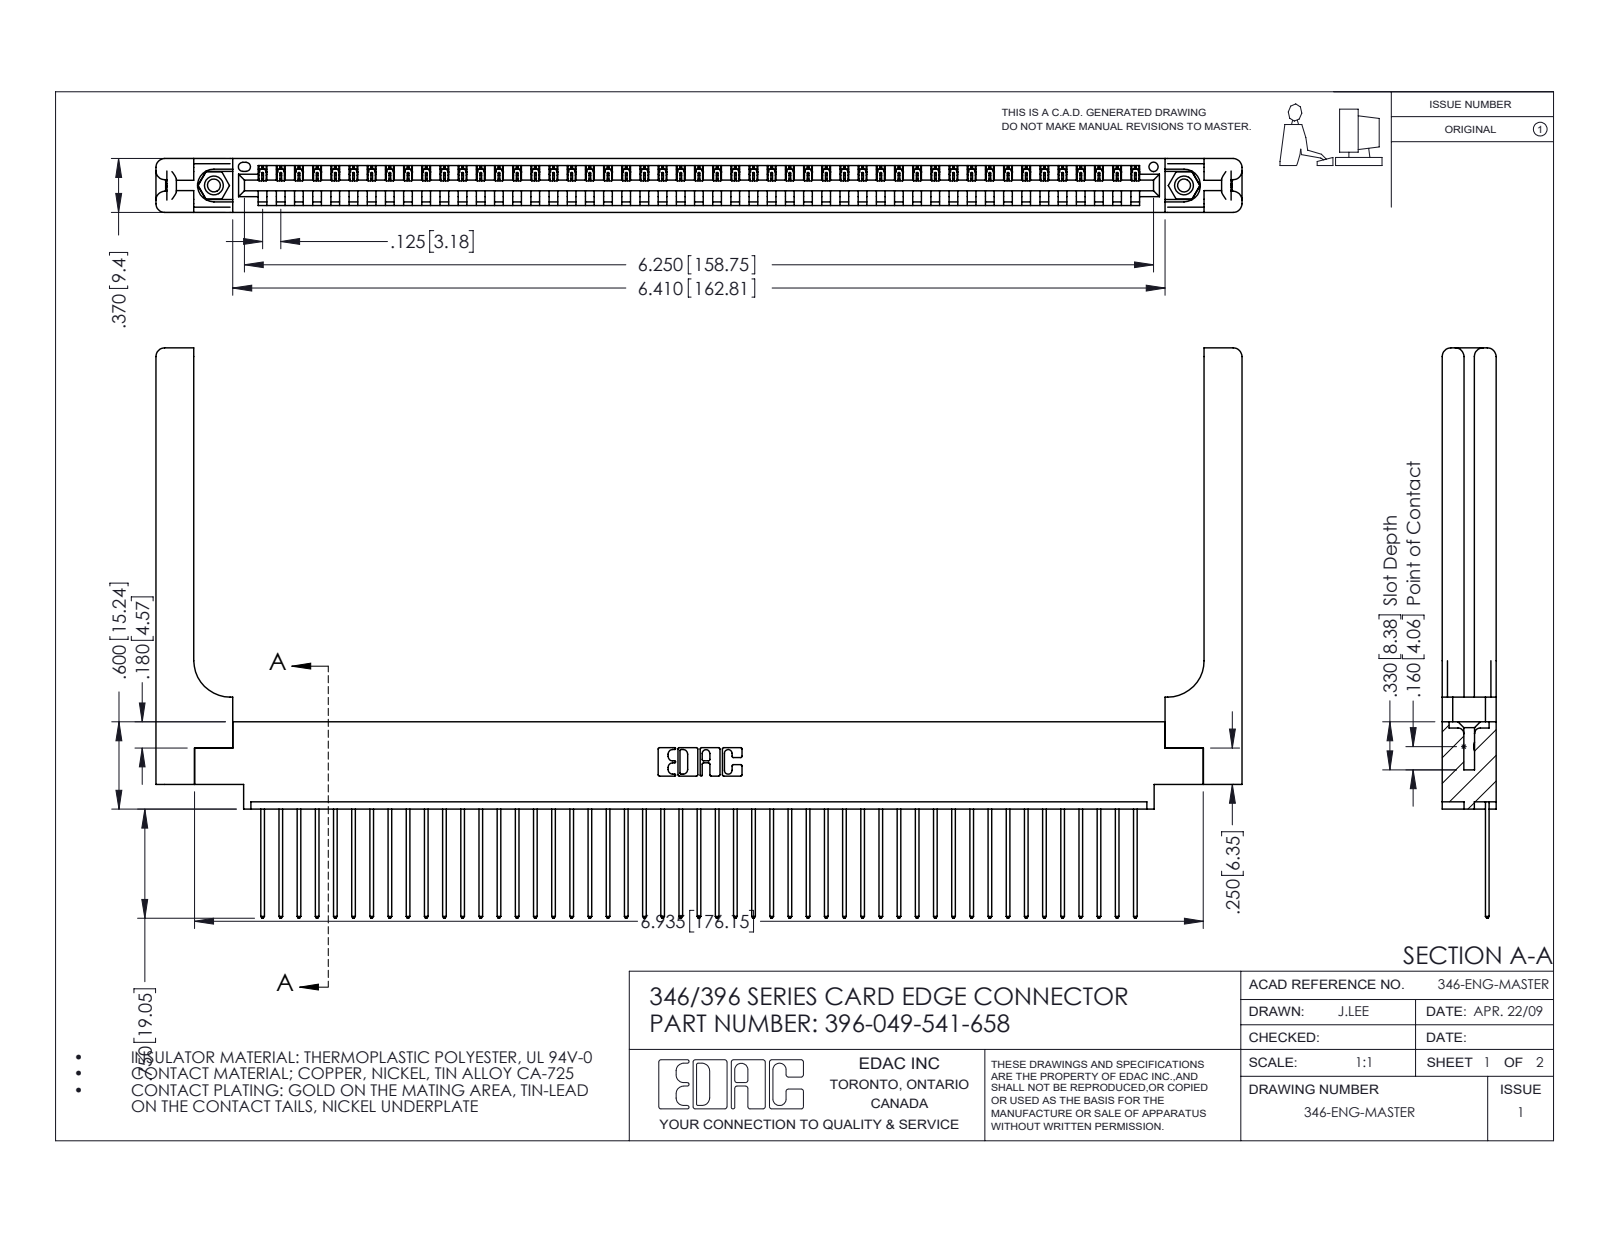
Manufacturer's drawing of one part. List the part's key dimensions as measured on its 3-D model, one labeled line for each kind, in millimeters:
Part name (STEP PRODUCT): 346 Part_0.170 Offset - 0.156 Dia-TH; 346-220-058_345-220-058; 345-250-001_345-250-001-102; 396-049-541-658 (+1 more)
STEP written by: SolidWorks 2016 (CONFIG_CONTROL_DESIGN)
Units: millimetres
Bodies: 54 solids, 3224 faces (2188 planar, 976 cylindrical, 60 other)
Overall size (bounding box): 189.6 × 99.6 × 9.4
Volume: 25 730 mm³ · Surface area: 29 130 mm²
Round holes (diameter × count): ⌀2.3 ×2, ⌀3.2 ×2, ⌀4 ×2, ⌀1.6 ×1
Round bosses / shafts (diameter × count): ⌀3.9 ×2
Partial cylindrical surfaces — rounded edges, fillets, slot ends (radius × count): R0.2 ×98, R0.3 ×98, R0.3 ×22, R1.5 ×16, R0.2 ×6, R0.8 ×6, R0.7 ×3, R0.8 ×2
Main face-to-face distances: 9.4, 1.2, 8.2, 1.8, 3.8, 7.6, 0.6, 3.8, 6.4, 5.6
Hole centre spacings: 6.2, 164.1, 169.4
